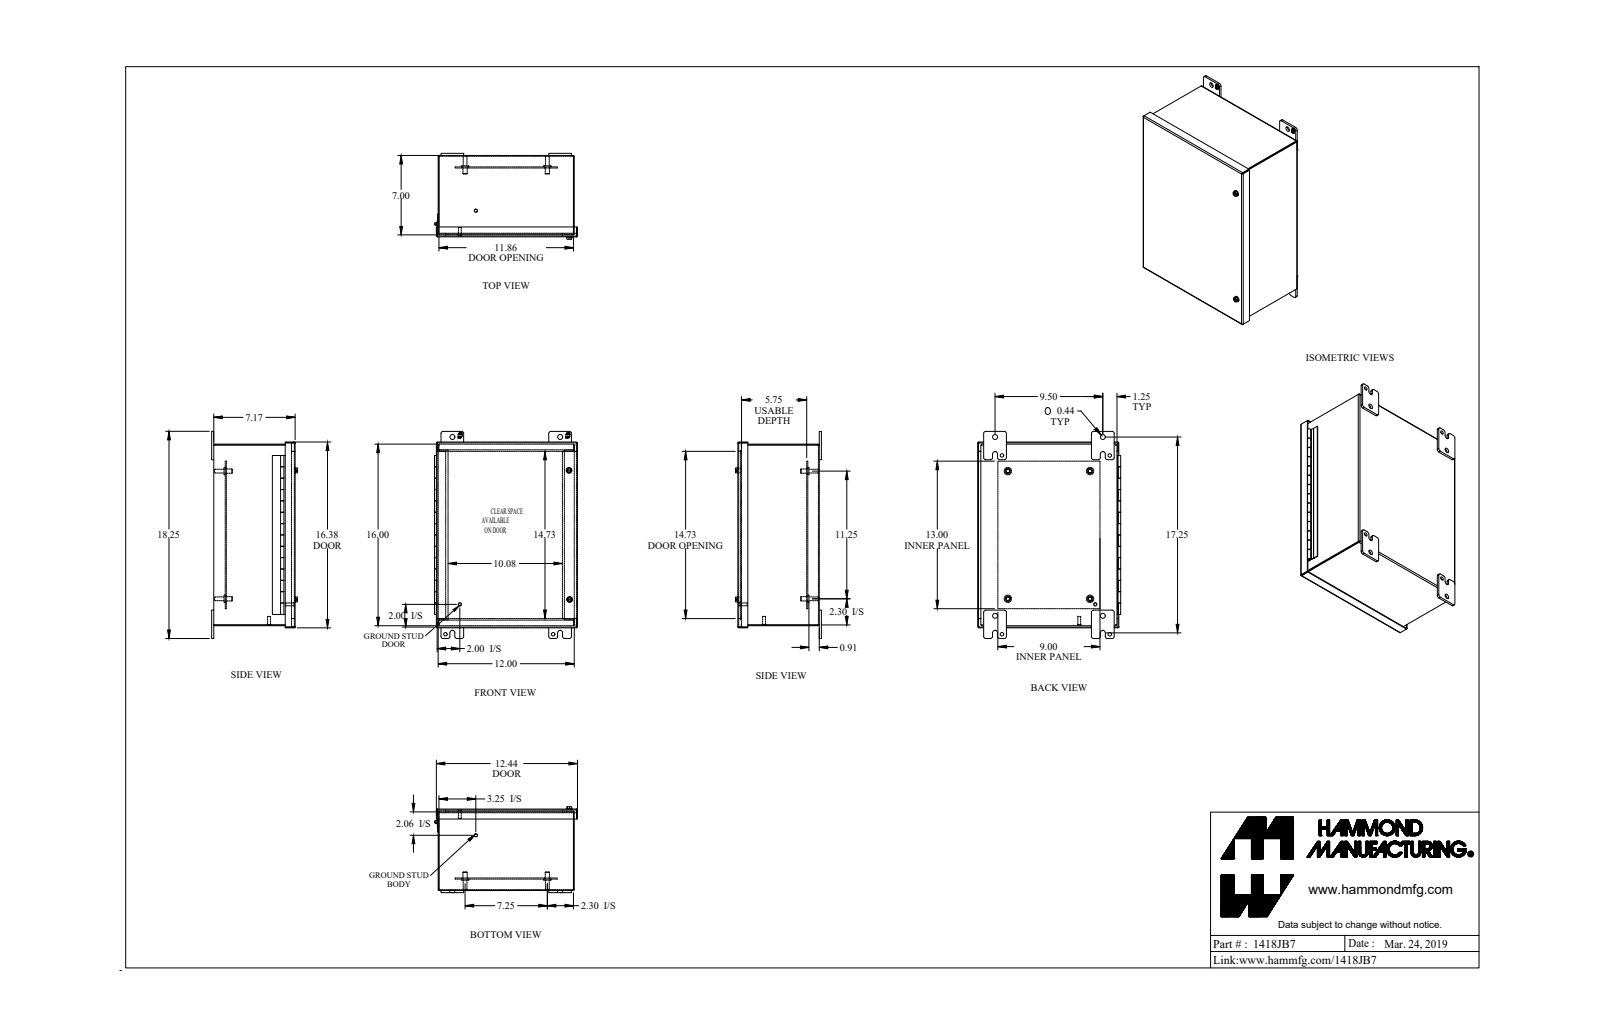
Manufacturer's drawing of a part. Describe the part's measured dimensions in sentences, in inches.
The part is named "1418JB7". Its 3-D file was written by "SolidWorks 2019 (AUTOMOTIVE_DESIGN)". It is 29 solids with 589 faces: 401 planar, 152 cylindrical and 36 other. Overall it measures 18.25 by 12.604 by 7.571 inches. Its volume is 91.05 cubic inches and its surface area 2 225 square inches. Round holes: 6 of diameter 0.313, 4 of diameter 0.437, 4 of diameter 0.5, 2 of diameter 0.26, 2 of diameter 0.266, 2 of diameter 0.307, 2 of diameter 0.397, 2 of diameter 0.445, 1 of diameter 0.187. Round bosses or shafts: 4 of diameter 0.65, 4 of diameter 0.375, 4 of diameter 0.33, 2 of diameter 1, 2 of diameter 0.541, 2 of diameter 0.51, 2 of diameter 0.281, 2 of diameter 0.25. Partial cylindrical surfaces (rounded edges, fillets, slot ends): 24 of radius 0.188, 12 of radius 0.007, 12 of radius 0.079, 8 of radius 0.05, 8 of radius 0.218, 2 of radius 0.029, 2 of radius 0.079, 2 of radius 0.125. The main face-to-face distances are 0.072, 7.1, 11.928, 7.172, 7.028, 15.928, 6.091, 1.104, 1.032, 5.996. The hole center spacings are 1.736, 9.5, 15.75, 18.393, 1.966, 3.204, 7.25, 9.038.
